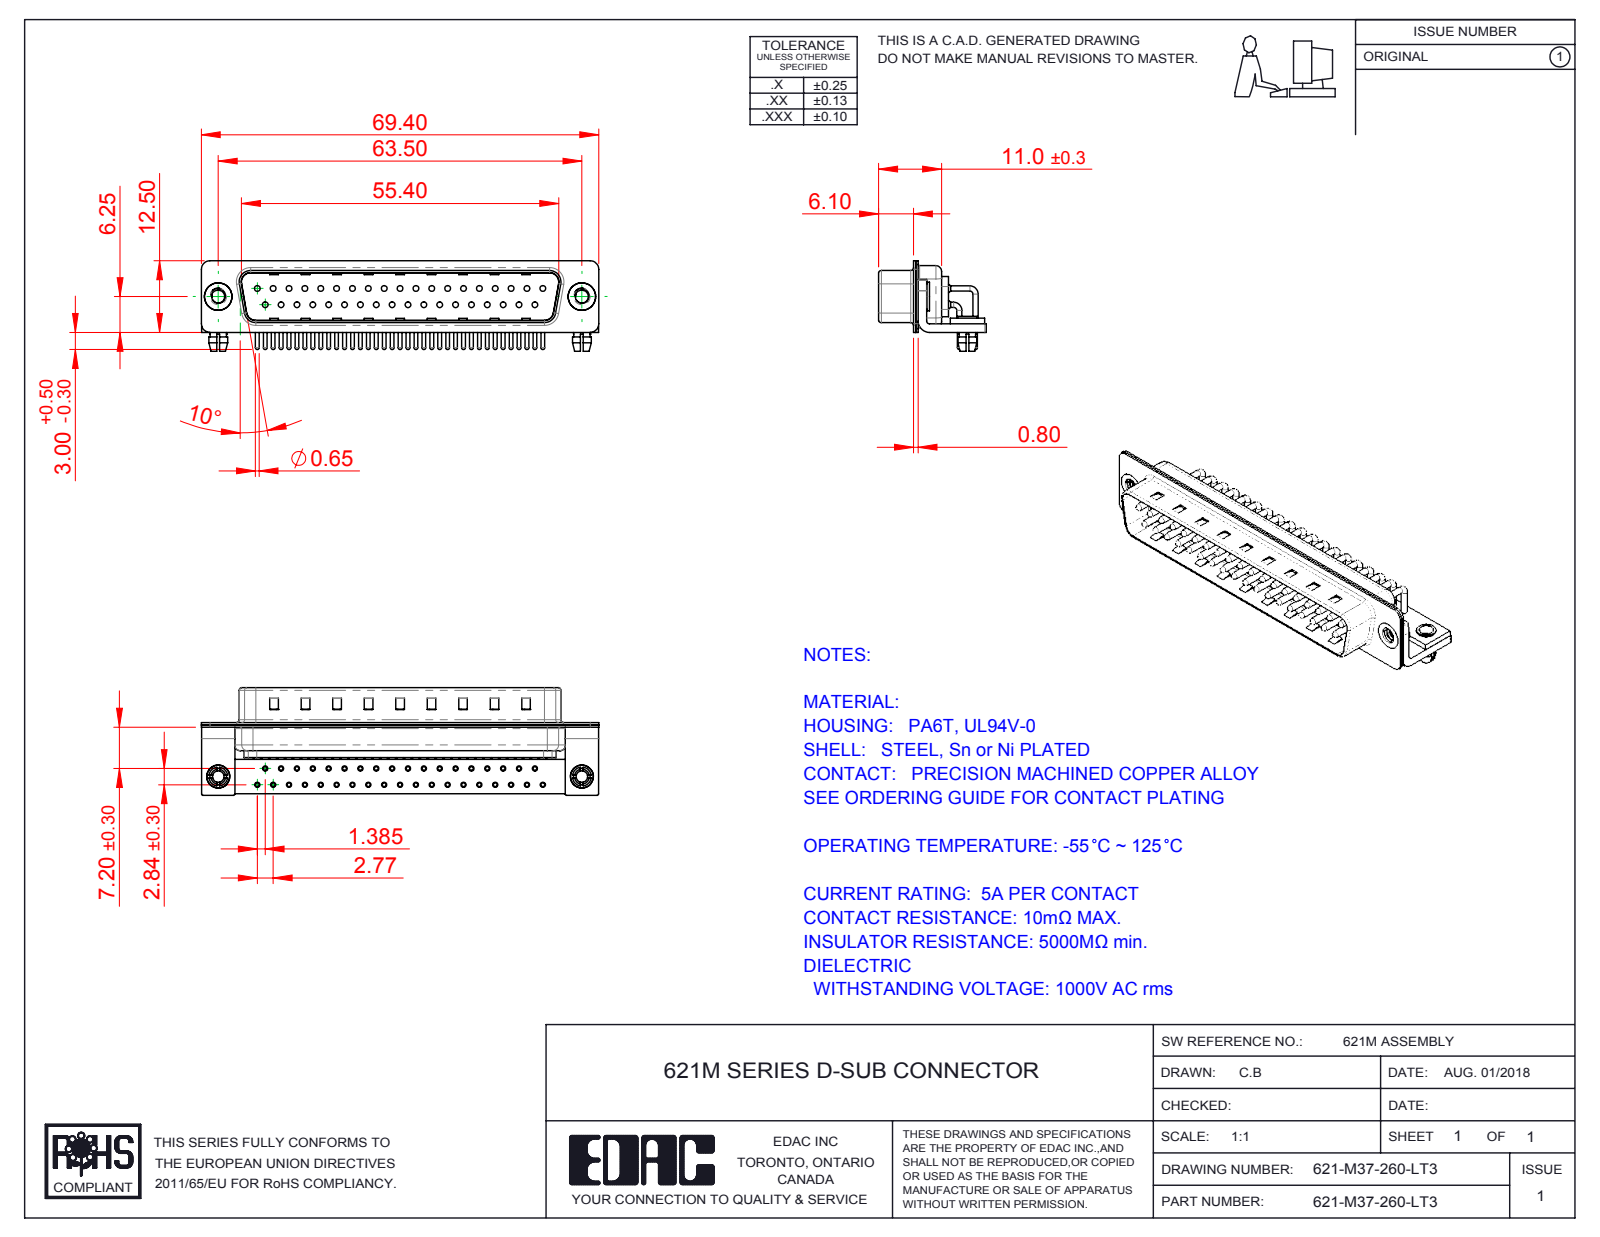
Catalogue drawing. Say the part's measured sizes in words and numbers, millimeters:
The part is named "621M Shell Rear_37 Contacts; 621M Contact Row 1; 621M Board Lock; 621M Contact Row 2 (+6 more)". Its 3-D file was written by "SolidWorks 2016 (CONFIG_CONTROL_DESIGN)". It is 47 solids with 4698 faces: 2645 planar, 1601 cylindrical and 452 other. Overall it measures 69.4 by 18.8 by 15.8 millimeters. Its volume is 4 643 cubic millimeters and its surface area 12 155 square millimeters. Round holes: 39 of diameter 2, 37 of diameter 0.9, 37 of diameter 1, 37 of diameter 1.7, 2 of diameter 2.26, 2 of diameter 2.5, 2 of diameter 3.2, 2 of diameter 4, 2 of diameter 4.8. Round bosses or shafts: 46 of diameter 0.9, 37 of diameter 1.5, 37 of diameter 0.65, 2 of diameter 5, 2 of diameter 4.9, 2 of diameter 4, 2 of diameter 3.4, 2 of diameter 3.3. Partial cylindrical surfaces (rounded edges, fillets, slot ends): 37 of radius 1.01, 16 of radius 0.25, 16 of radius 1.5, 13 of radius 2, 9 of radius 0.5, 8 of radius 1.6, 4 of radius 0.6, 4 of radius 0.65. The main face-to-face distances are 0.4, 0.85, 1.25, 9.55, 1.5, 10.4, 8.3, 0.8, 8.7, 1. The hole center spacings are 3.16, 2.77, 5.54, 8.31, 11.08, 13.85, 5.03, 16.62.
